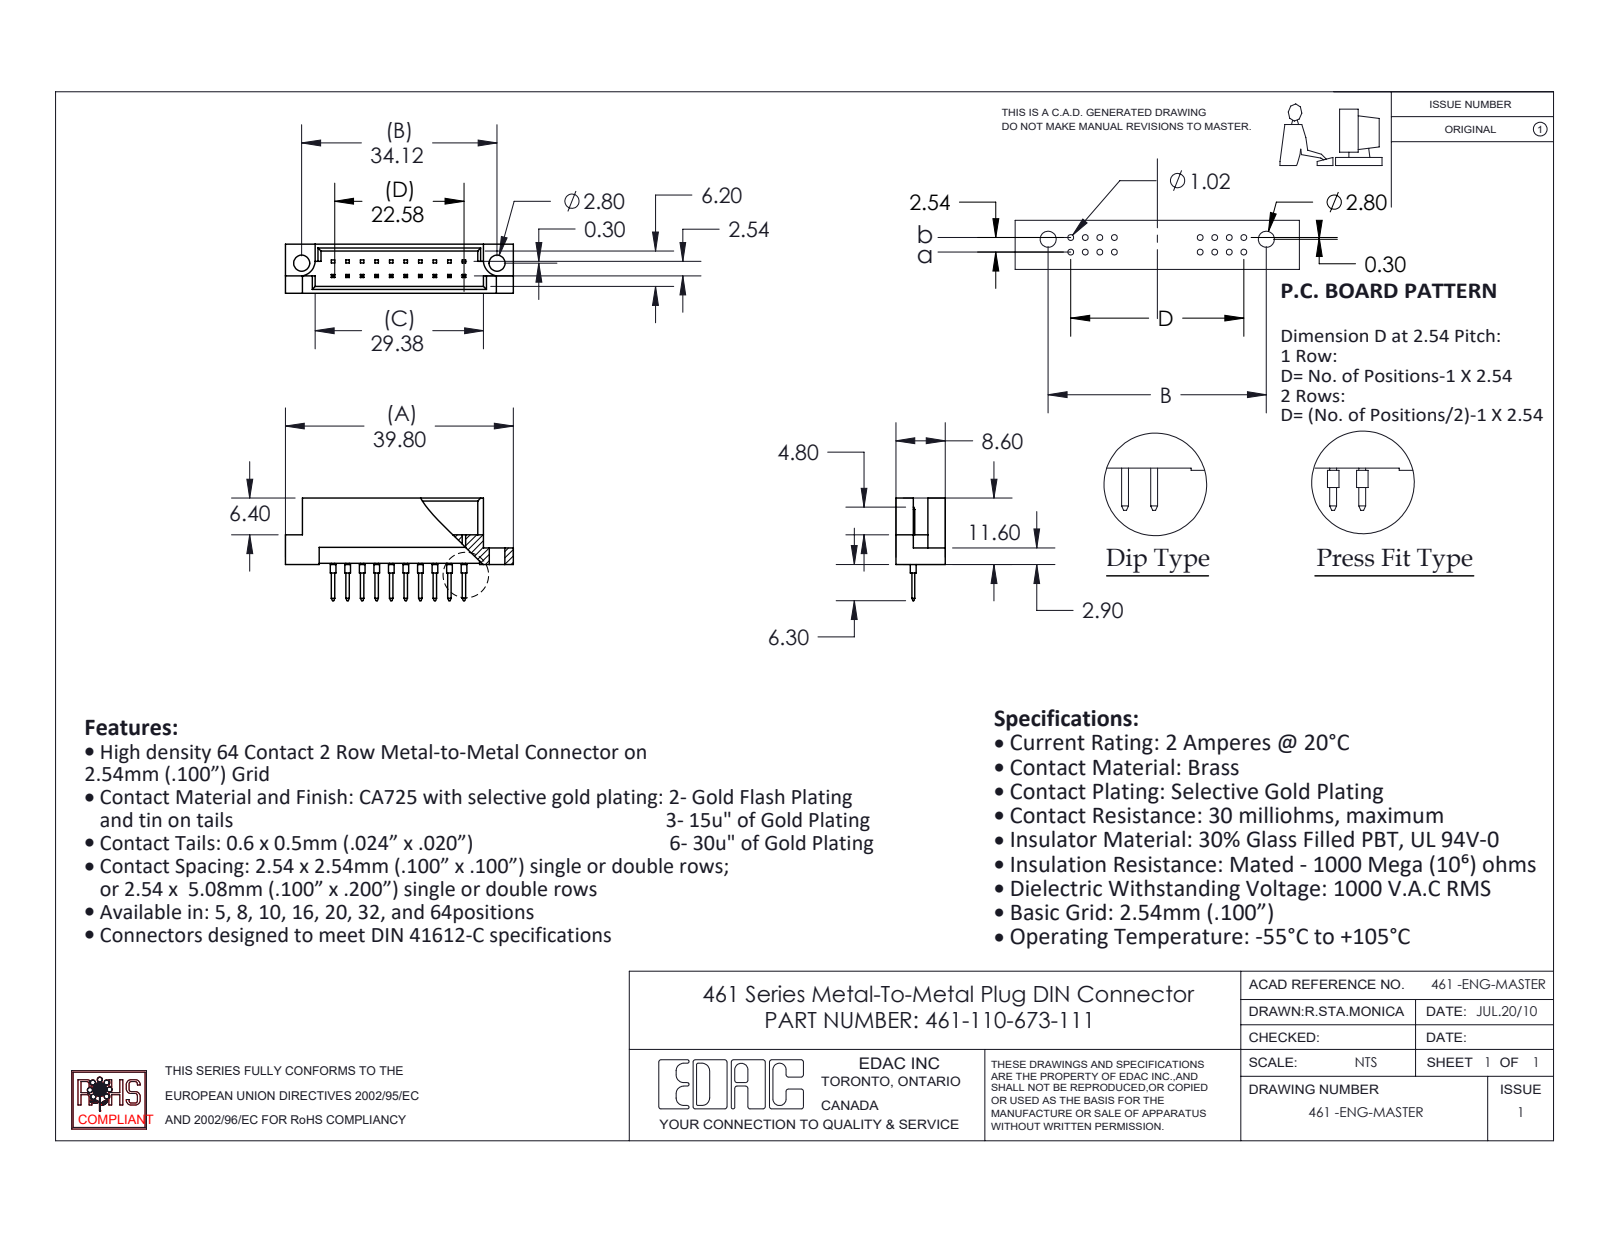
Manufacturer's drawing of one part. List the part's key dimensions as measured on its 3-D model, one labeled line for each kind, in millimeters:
Part name (STEP PRODUCT): 461-110-673-111; 461-290_73; 461 Part_20
STEP written by: SolidWorks 2020 (CONFIG_CONTROL_DESIGN)
Units: millimetres
Bodies: 11 solids, 348 faces (322 planar, 26 cylindrical, 0 other)
Overall size (bounding box): 39.8 × 17.9 × 8.6
Volume: 1 960 mm³ · Surface area: 2 716 mm²
Round holes (diameter × count): ⌀2.8 ×2
Round bosses / shafts (diameter × count): ⌀1 ×10
Partial cylindrical surfaces — rounded edges, fillets, slot ends (radius × count): R2.8 ×2
Main face-to-face distances: 1.2, 7.4, 8.6, 6.2, 2.54, 5, 2.78, 3.28, 5.32, 5.82
Hole centre spacings: 34.12
